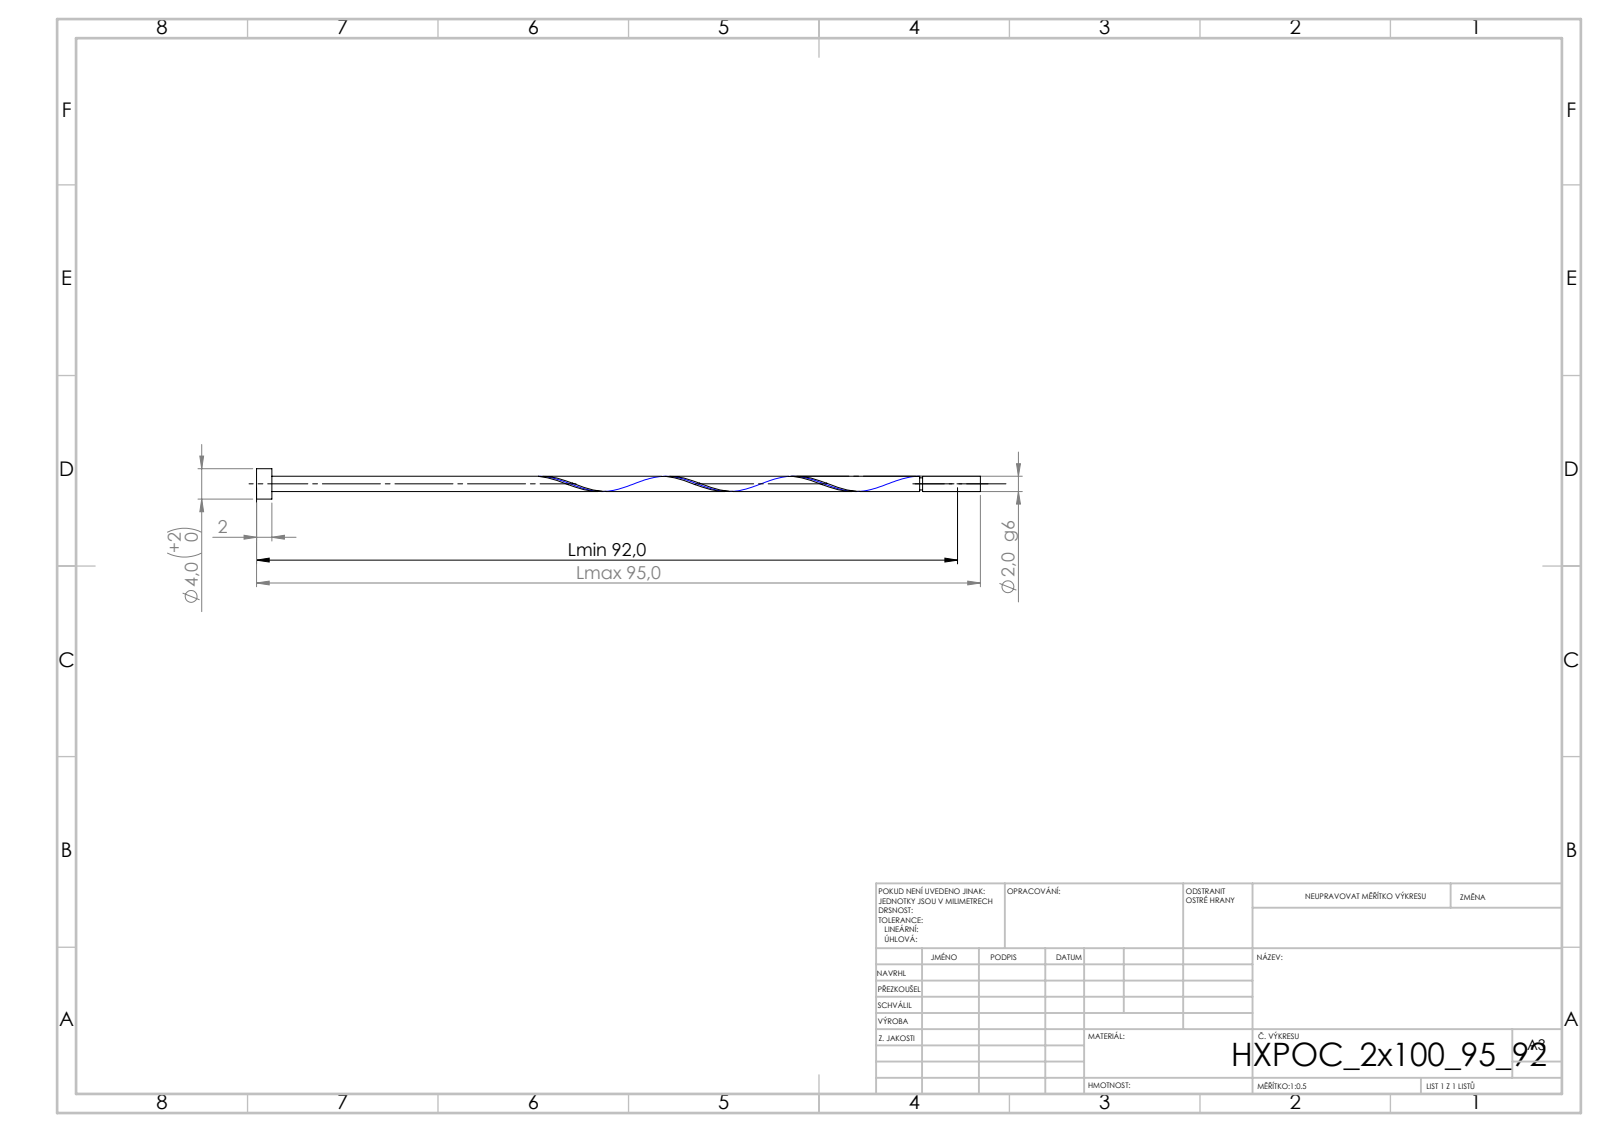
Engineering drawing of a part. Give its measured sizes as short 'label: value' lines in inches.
written by: SolidWorks 2019 (CONFIG_CONTROL_DESIGN)
unit: in
bodies: 1 solid, 21 faces (6 planar, 14 cylindrical, 1 other)
size: 3.74 × 0.157 × 0.157
volume: 0.019 in³; area: 1 in²
bosses: 1× ⌀0.157, 1× ⌀0.079, 1× ⌀0.063
face distances: 0.079, 3.74, 3.661, 3.442, 3.363, 0.298, 3.426, 3.347, 0.016, 0.314
